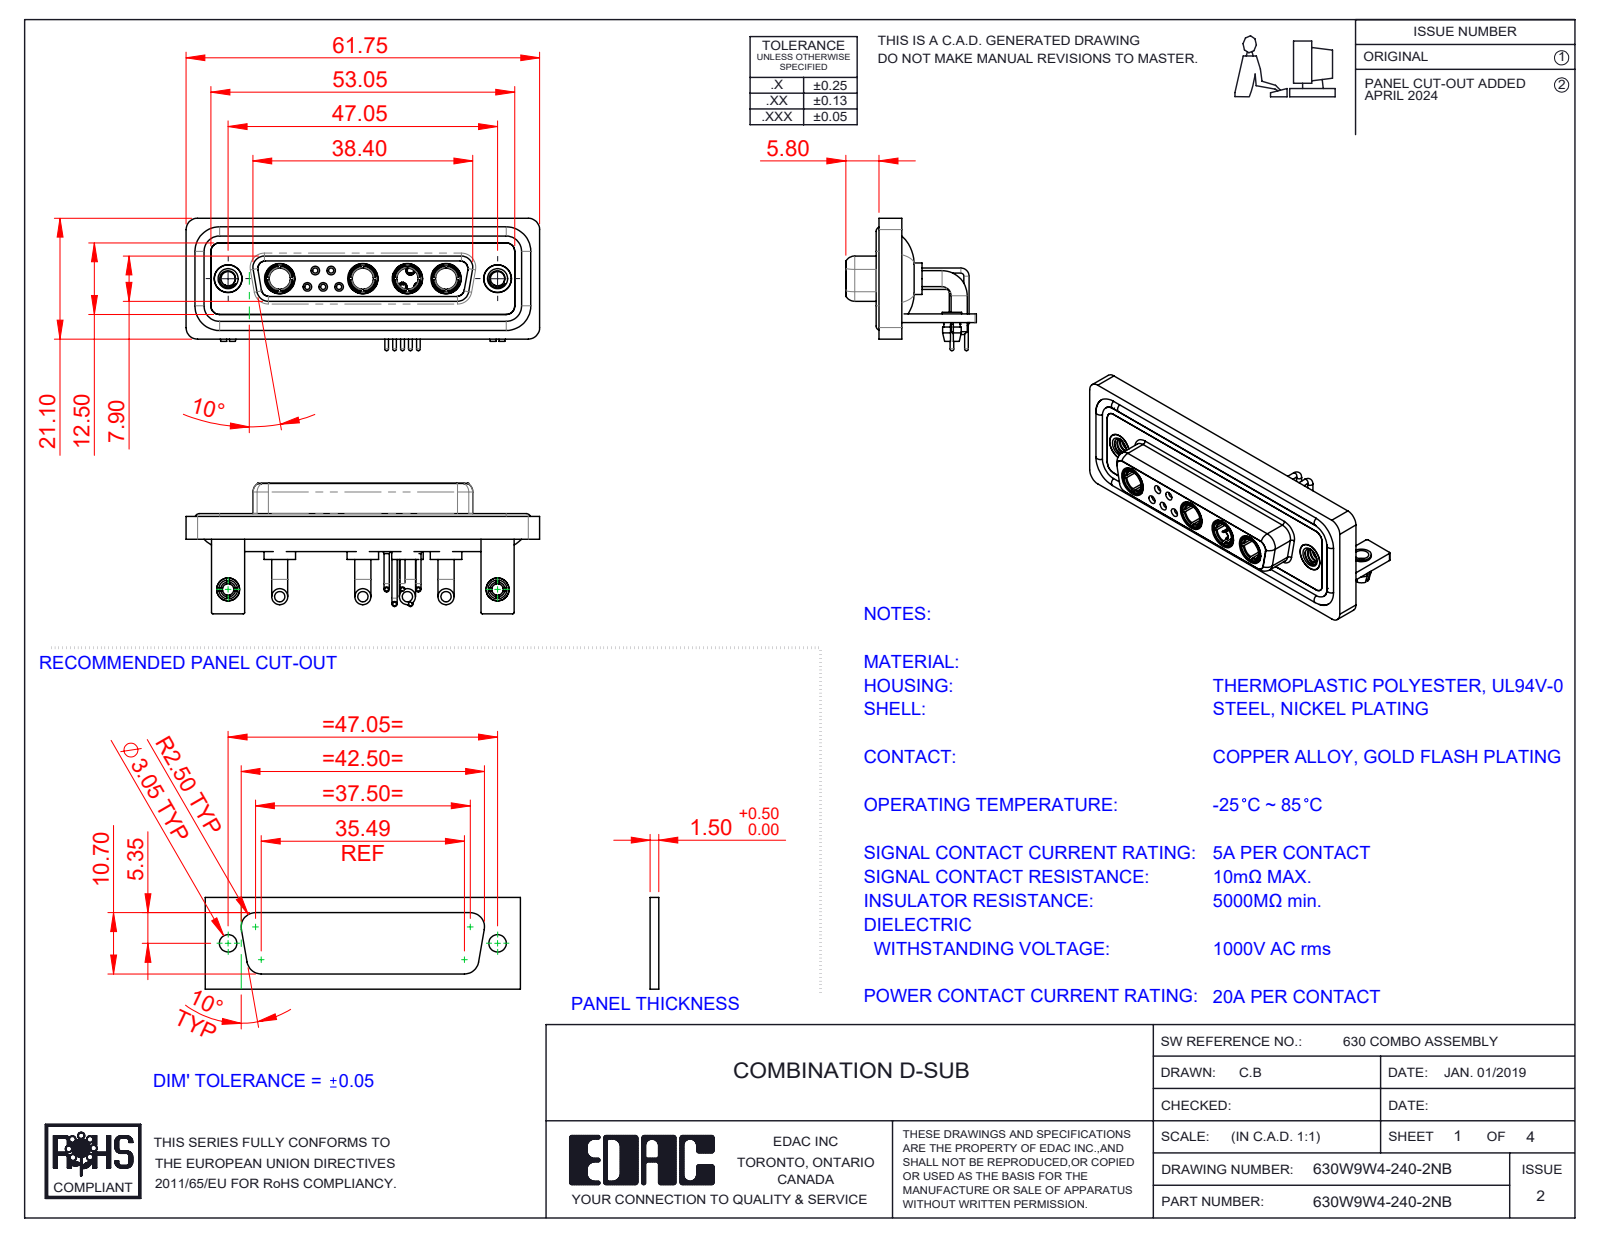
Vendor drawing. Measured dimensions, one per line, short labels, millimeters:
name: Power Socket_20A RA; 630Combo Housing_9W4; 630Combo Contact Row 1_50 Contacts; 630Combo Contact Row 2_50 Contacts (+7 more)
written by: SolidWorks 2023 (CONFIG_CONTROL_DESIGN)
unit: mm
bodies: 24 solids, 1097 faces (364 planar, 457 cylindrical, 276 other)
size: 61.75 × 23.12 × 22.8
volume: 8 847 mm³; area: 14 996 mm²
holes: 7× ⌀2, 6× ⌀4.85, 5× ⌀0.9, 5× ⌀1.1, 5× ⌀1.5, 4× ⌀2.5, 4× ⌀3.7, 4× ⌀5.3, 3× ⌀1.6, 2× ⌀1.7, 2× ⌀3.2, 2× ⌀4
bosses: 10× ⌀0.9, 9× ⌀1.6, 8× ⌀2.8, 5× ⌀2, 5× ⌀1.5, 5× ⌀0.65, 4× ⌀5.5, 4× ⌀5.2
rounds: 19× R2, 18× R1.5, 16× R0.25, 8× R1.35, 8× R1.6, 5× R0.5, 4× R0.6, 4× R0.65
face distances: 0.4, 1.8, 2.9, 3.7, 1.5, 4.1, 1.1, 1.4, 1.6, 2.5
hole spacings: 3.16, 2.77, 5.04, 13.85, 11.08, 12.79, 15.5, 5.54
